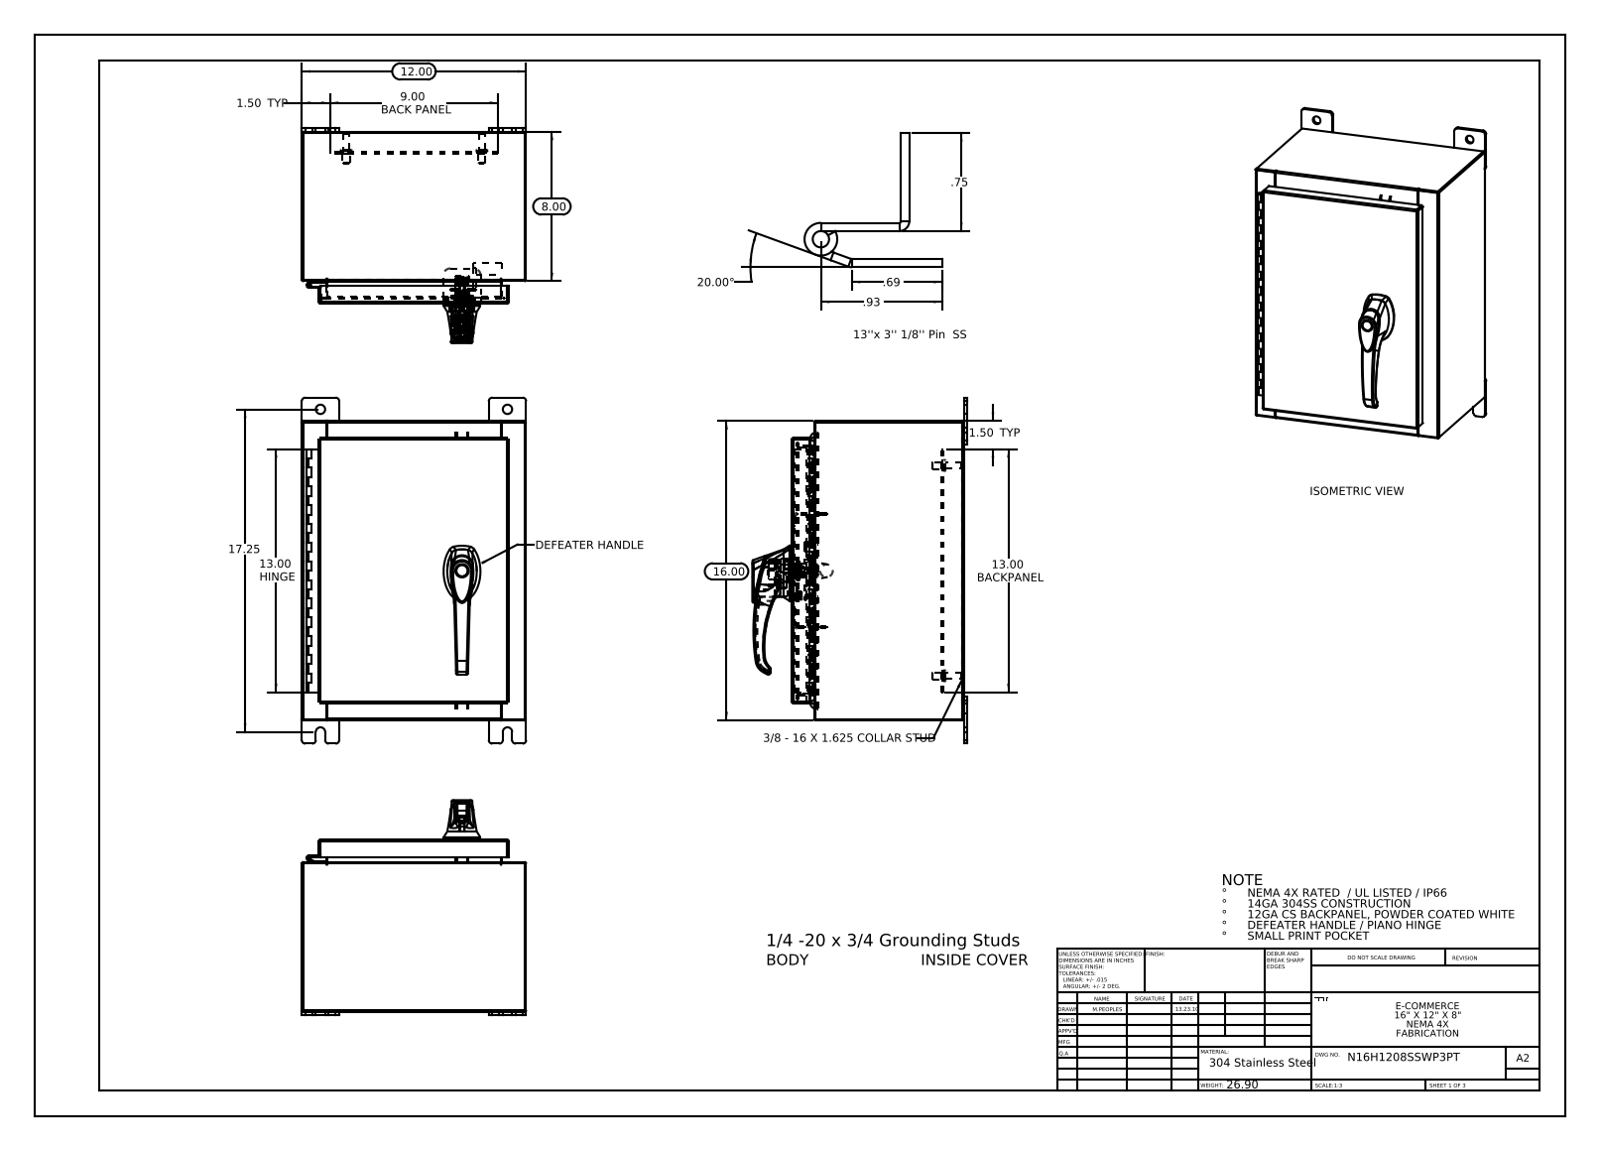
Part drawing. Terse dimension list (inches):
name: N16H1208SSWP3PT Bottom; g26103103_26163303; 00005090; NMP-SS-RODGUIDES (+8 more)
written by: SolidWorks 2013 (CONFIG_CONTROL_DESIGN)
unit: in
bodies: 31 solids, 2204 faces (757 planar, 793 cylindrical, 654 other)
size: 18.5 × 12 × 11.495
volume: 97.14 in³; area: 2 391 in²
holes: 8× ⌀0.5, 4× ⌀0.25, 3× ⌀0.138, 3× ⌀0.161, 2× ⌀0.079, 2× ⌀0.203, 2× ⌀0.313, 2× ⌀0.437, 1× ⌀0.125, 1× ⌀0.125, 1× ⌀0.197, 1× ⌀0.276
bosses: 4× ⌀0.625, 4× ⌀0.375, 4× ⌀0.33, 1× ⌀1.181, 1× ⌀0.748, 1× ⌀0.68, 1× ⌀0.661, 1× ⌀0.639
rounds: 37× R0.118, 33× R0.006, 24× R0.19, 20× R0.013, 18× R0.088, 15× R0.039, 12× R0.028, 6× R0.008
face distances: 0.075, 9.126, 11.925, 15.925, 9.051, 9.201, 7.925, 1.201, 11.85, 12
hole spacings: 3.708, 0.295, 0.625, 0.841, 1.25, 1.313, 1.32, 1.484
